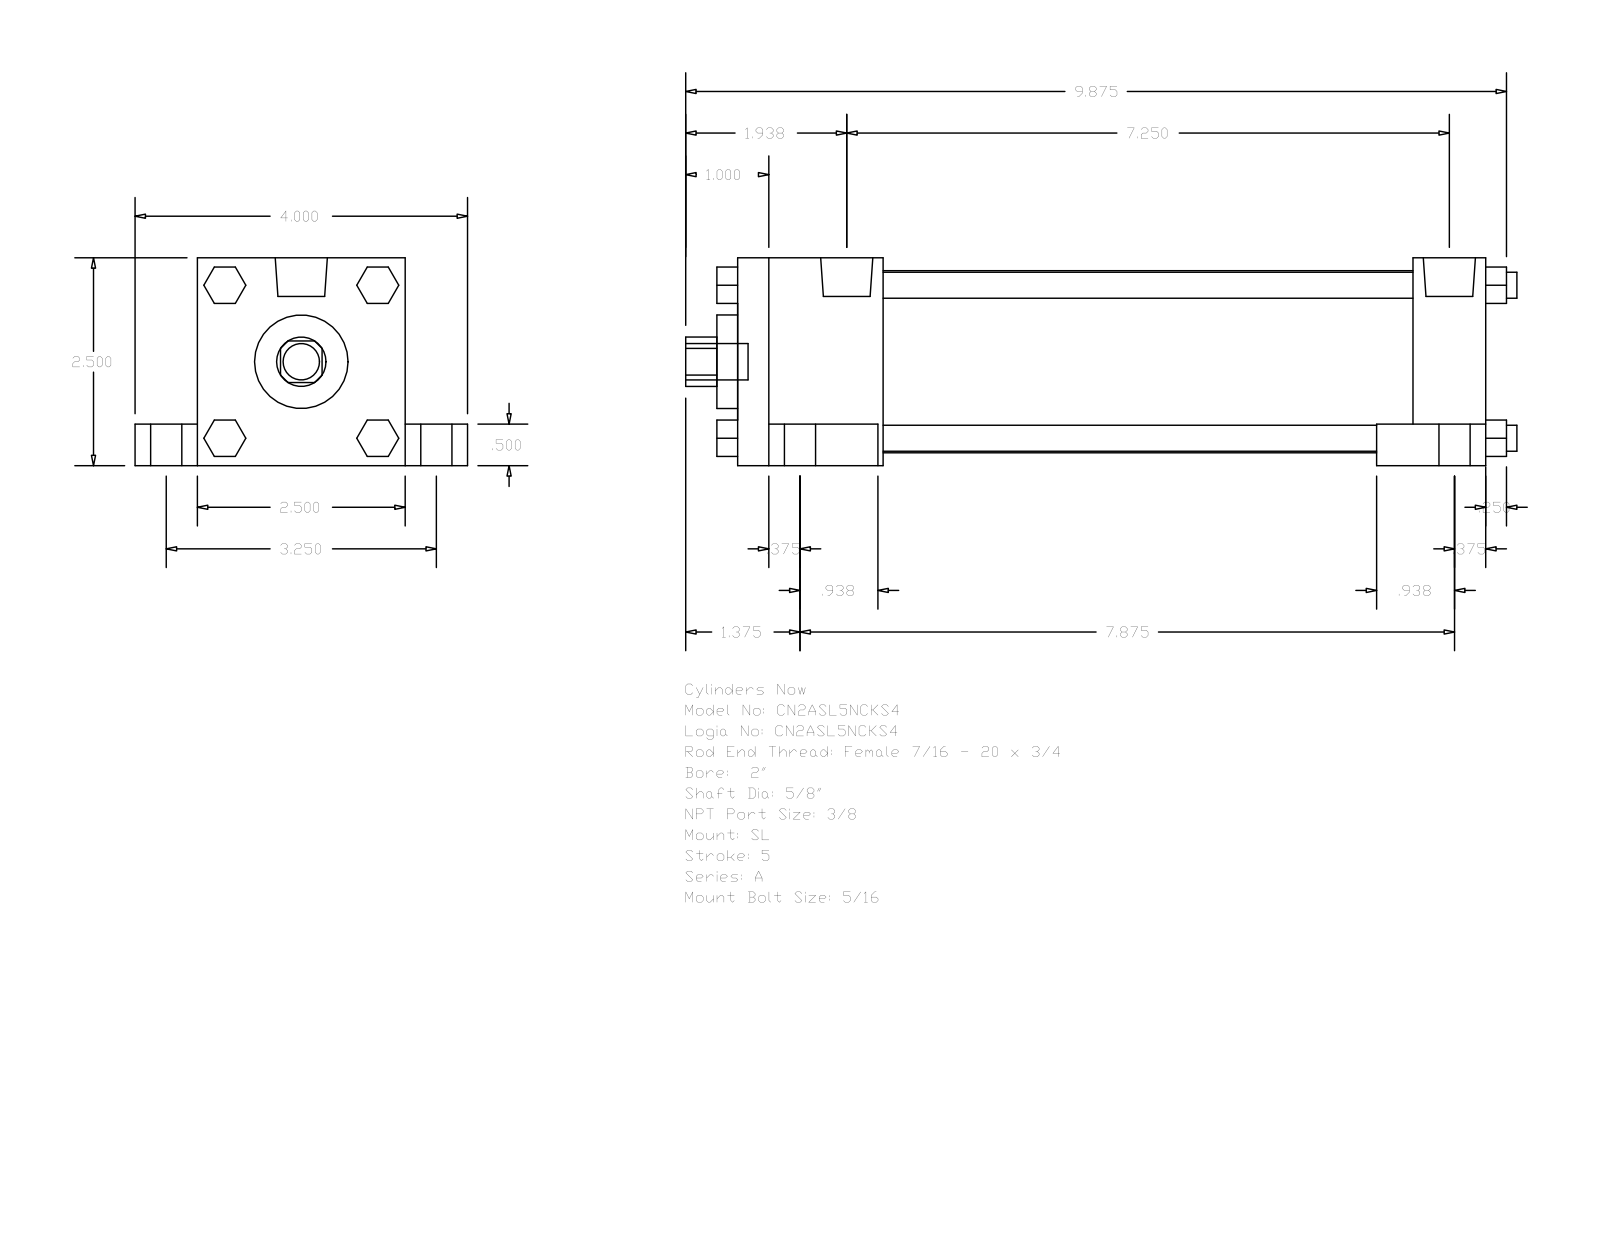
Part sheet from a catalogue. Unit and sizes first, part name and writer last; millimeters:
Units: millimetres
Overall size (bounding box): 254 × 101.6 × 63.5
Round holes (diameter × count): ⌀15.88 ×1, ⌀28.57 ×1, ⌀55.63 ×1
Round bosses / shafts (diameter × count): ⌀15.88 ×4, ⌀9.53 ×4, ⌀7.94 ×4, ⌀5.56 ×4, ⌀15.93 ×2, ⌀11.11 ×1
Partial cylindrical surfaces — rounded edges, fillets, slot ends (radius × count): R7.54 ×1
Main face-to-face distances: 63.5, 228.59, 50.8, 12.7, 19.05, 82.55, 44.45, 184.14, 206.37, 161.92
Bodies: 0 solids, 148 faces (112 planar, 36 cylindrical, 0 other)
Part name (STEP PRODUCT): A_SL__0200_0.625
STEP written by: GSSL Pune (CONFIG_CONTROL_DESIGN)
